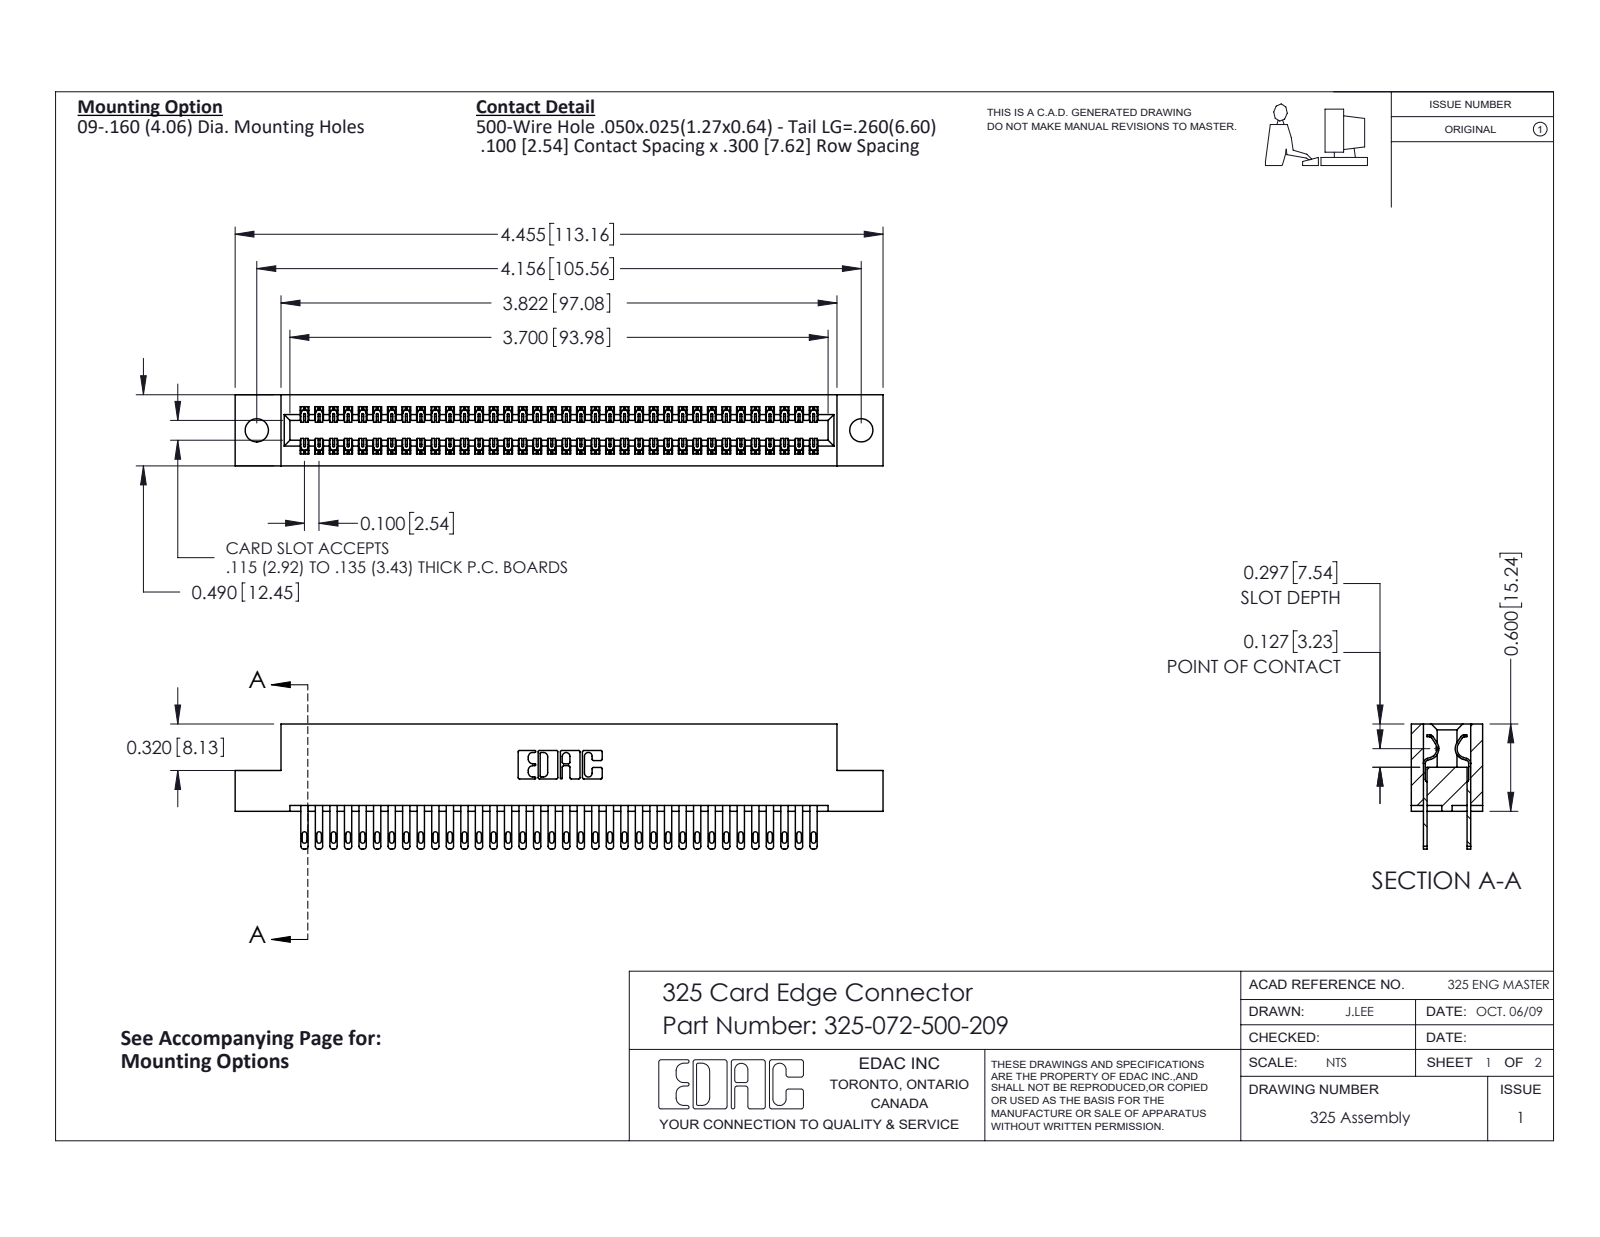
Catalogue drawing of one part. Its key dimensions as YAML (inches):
part_name: "325-292-001_325-293-100; 325-072-500-209; 325 Part_.160 TH"
step_written_by: "SolidWorks 2016 (CONFIG_CONTROL_DESIGN)"
units: inches
bodies: {solids: 73, faces: 3570, planar: 2230, cylindrical: 1340, other: 0}
overall_size: [4.455, 0.86, 0.49]
volume: 0.887
surface_area: 28.11
round_holes:
  - {diameter: 0.16, count: 2}
partial_cylinders:
  - {radius: 0.006, count: 108}
  - {radius: 0.016, count: 72}
  - {radius: 0.02, count: 72}
  - {radius: 0.01, count: 22}
  - {radius: 0.007, count: 6}
  - {radius: 0.031, count: 6}
  - {radius: 0.026, count: 3}
  - {radius: 0.014, count: 2}
face_to_face_distances: [0.083, 0.407, 0.3, 0.107, 0.383, 0.025, 0.49, 0.325, 0.275, 0.56]
hole_center_spacings: [4.156]
